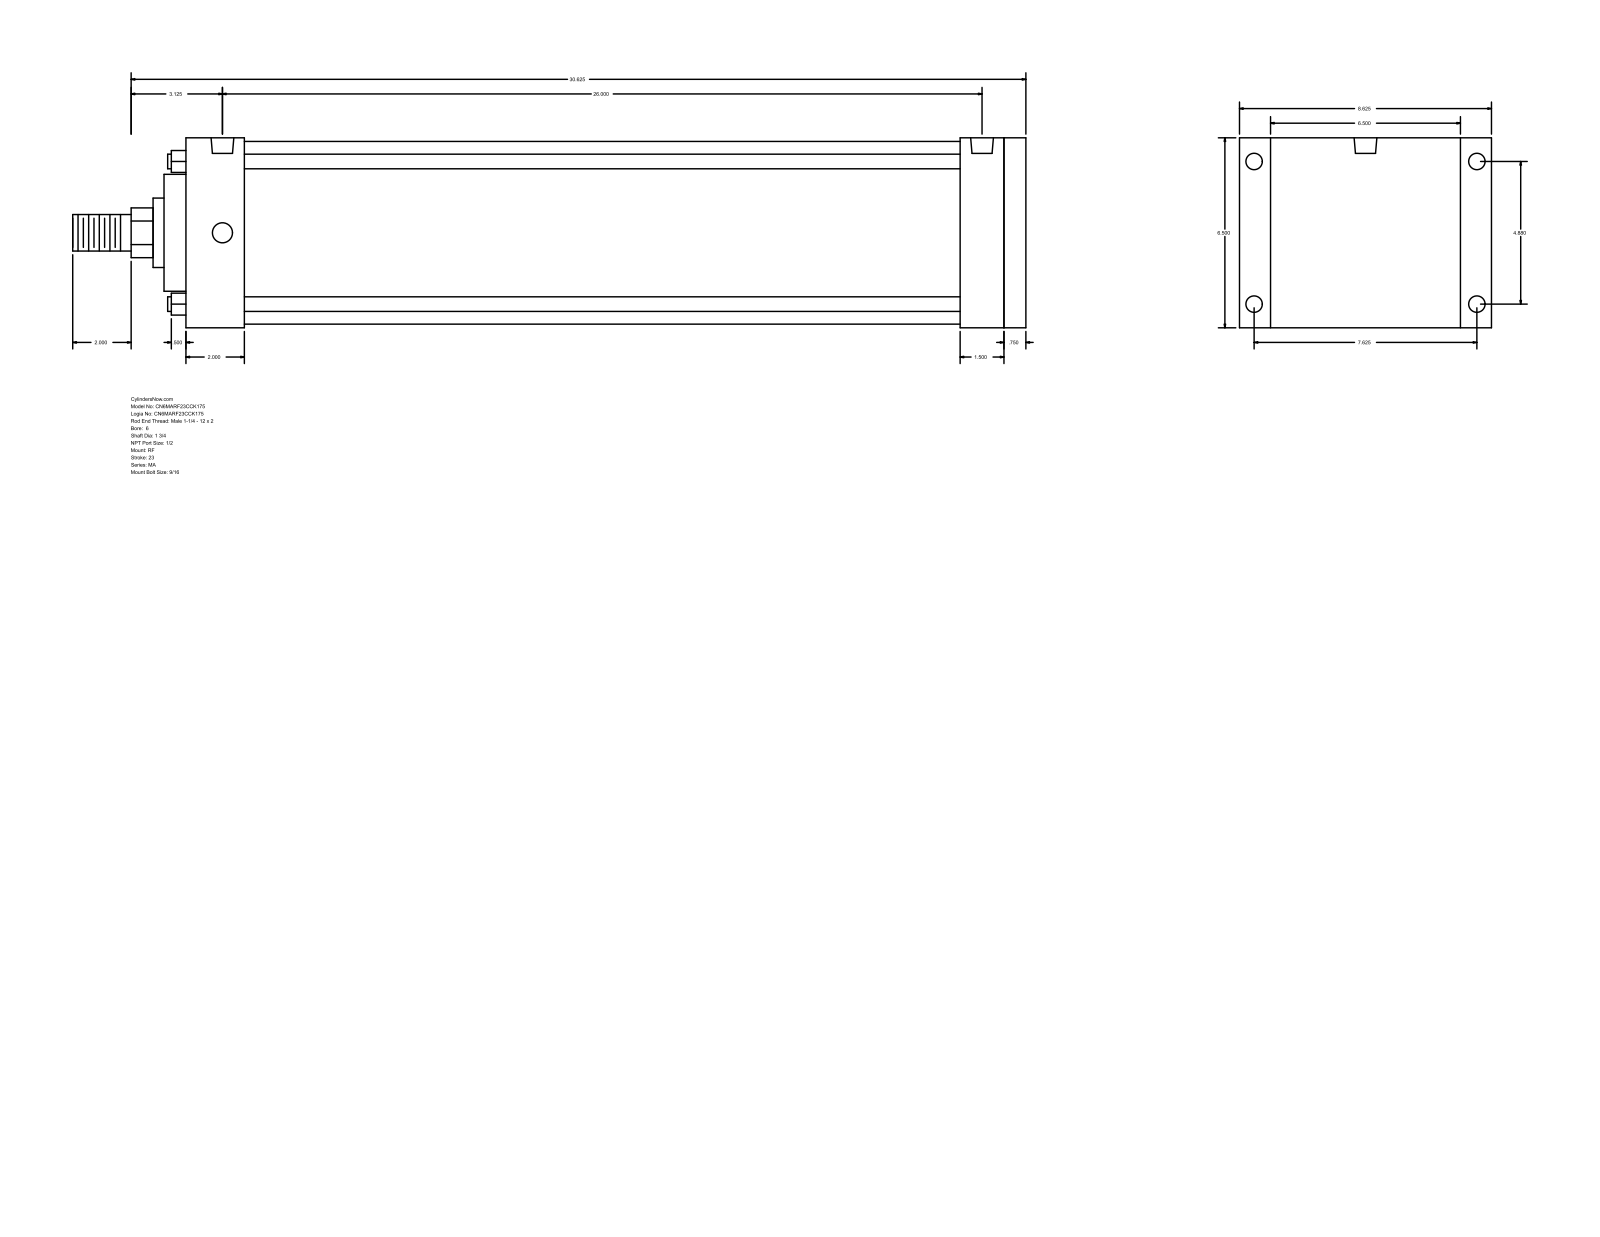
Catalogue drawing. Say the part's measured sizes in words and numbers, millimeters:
The part is named "MA_RF__0600_1.75". Its 3-D file was written by "GSSL Pune (CONFIG_CONTROL_DESIGN)". It is 0 solids with 94 faces: 65 planar, 29 cylindrical and 0 other. Overall it measures 828.67 by 219.07 by 165.1 millimeters. Round holes: 4 of diameter 14.29, 4 of diameter 17.46, 2 of diameter 19.77. Round bosses or shafts: 4 of diameter 12.7, 1 of diameter 158.75, 1 of diameter 101.6, 1 of diameter 60.33, 1 of diameter 44.45, 1 of diameter 31.75. Partial cylindrical surfaces (rounded edges, fillets, slot ends): 1 of radius 21.63. The main face-to-face distances are 165.1, 730.26, 19.05, 711.21, 38.1, 50.8, 660.41, 679.46, 673.11, 622.31. The hole center spacings are 123.96, 193.68, 229.95, 660.39.
